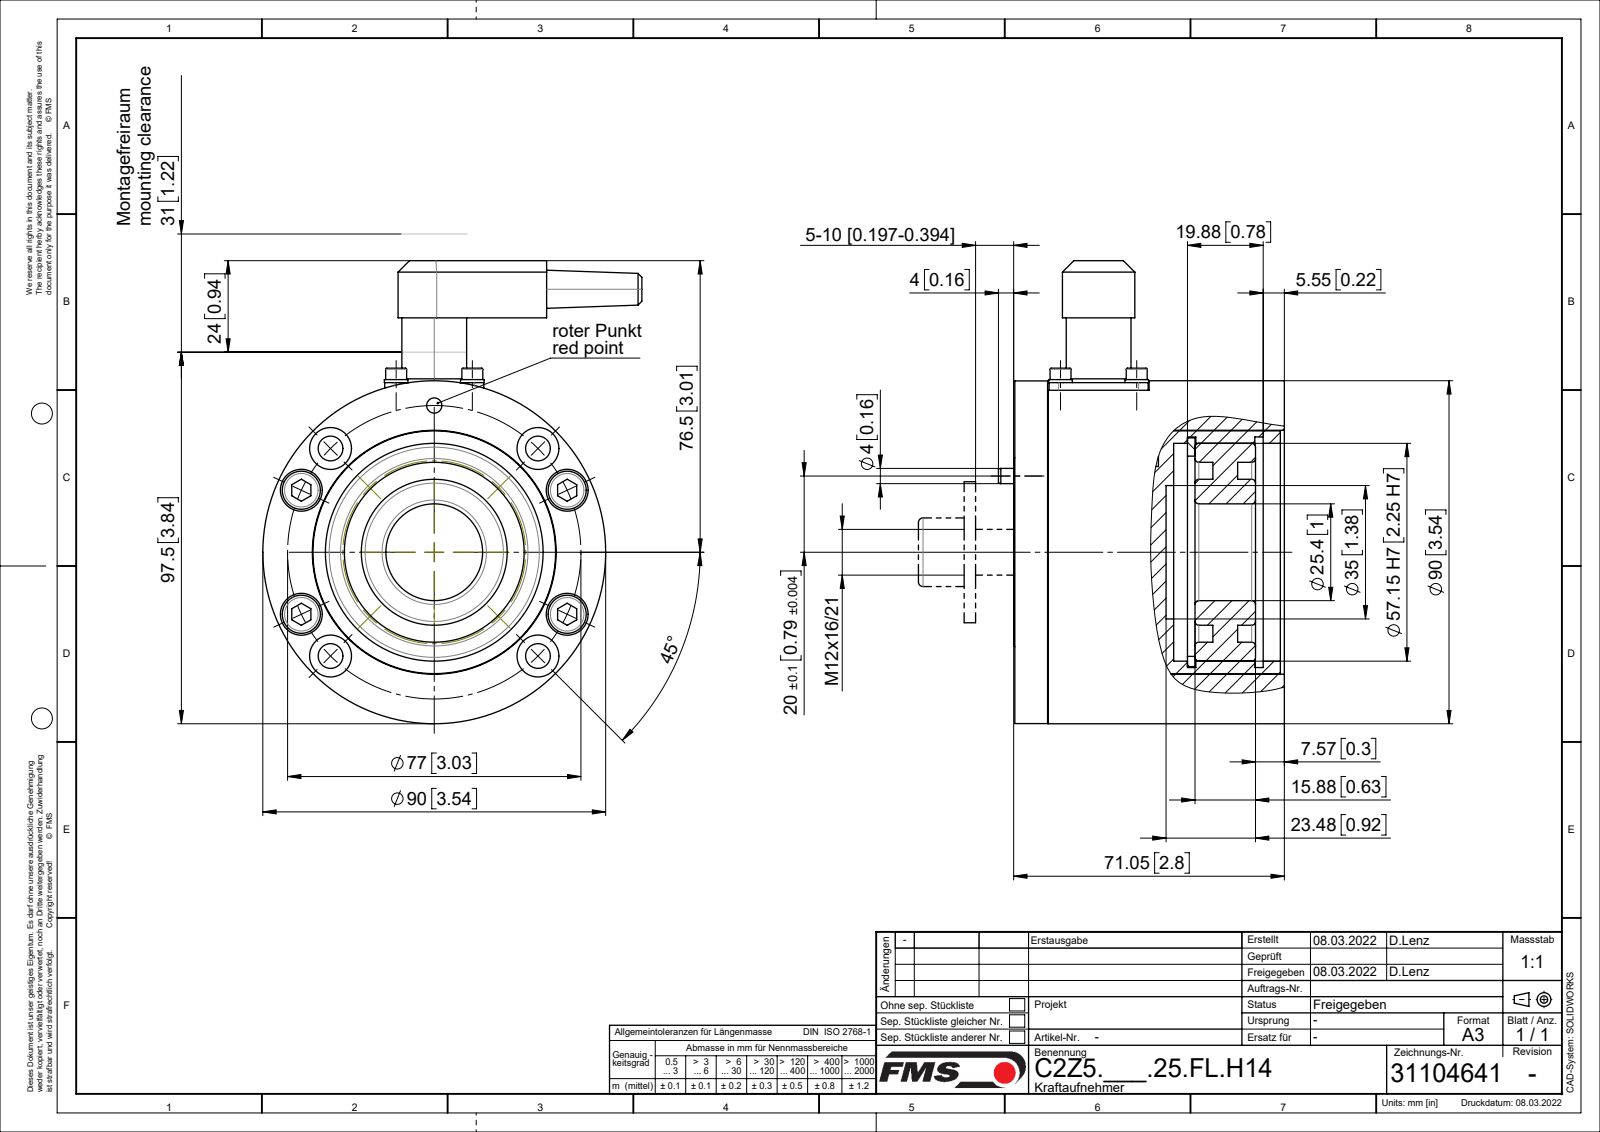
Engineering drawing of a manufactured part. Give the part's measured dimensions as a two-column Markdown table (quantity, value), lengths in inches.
| quantity | value |
| --- | --- |
| part name | 31104641; 31100948_01; Si-Ring DIN472_D57.15; Spannstift_ISO13337_D04x10 (+8 more) |
| STEP written by | SolidWorks 2018 (CONFIG_CONTROL_DESIGN) |
| units | inches |
| bodies | 22 solids, 565 faces (193 planar, 261 cylindrical, 111 other) |
| overall size | 4.783 × 3.917 × 3.781 |
| volume | 19.47 in³ |
| surface area | 193.8 in² |
| round holes (diameter × count) | 0.256 × 8, 0.433 × 8, 0.098 × 6, 0.079 × 5, 0.122 × 4, 0.126 × 4, 0.197 × 4, 0.276 × 4, 0.157 × 2, 0.118 × 1, 0.402 × 1, 0.472 × 1 |
| round bosses / shafts (diameter × count) | 0.059 × 5, 0.394 × 4, 0.244 × 4, 0.236 × 4, 0.217 × 4, 0.118 × 4, 3.543 × 1, 3.539 × 1 |
| partial cylindrical surfaces (radius × count) | 0.004 × 4, 0.098 × 4, 0.02 × 2, 0.164 × 2, 0.197 × 2, 0.374 × 1, 0.913 × 1, 1.035 × 1 |
| main face-to-face distances | 0.236, 1.26, 1.301, 0.079, 1.496, 0.339, 1.146, 1.484, 0.114, 0.224 |
| hole center spacings | 0.787, 1.516, 0.526, 0.557, 1.515, 1.739, 2.143, 2.483 |
